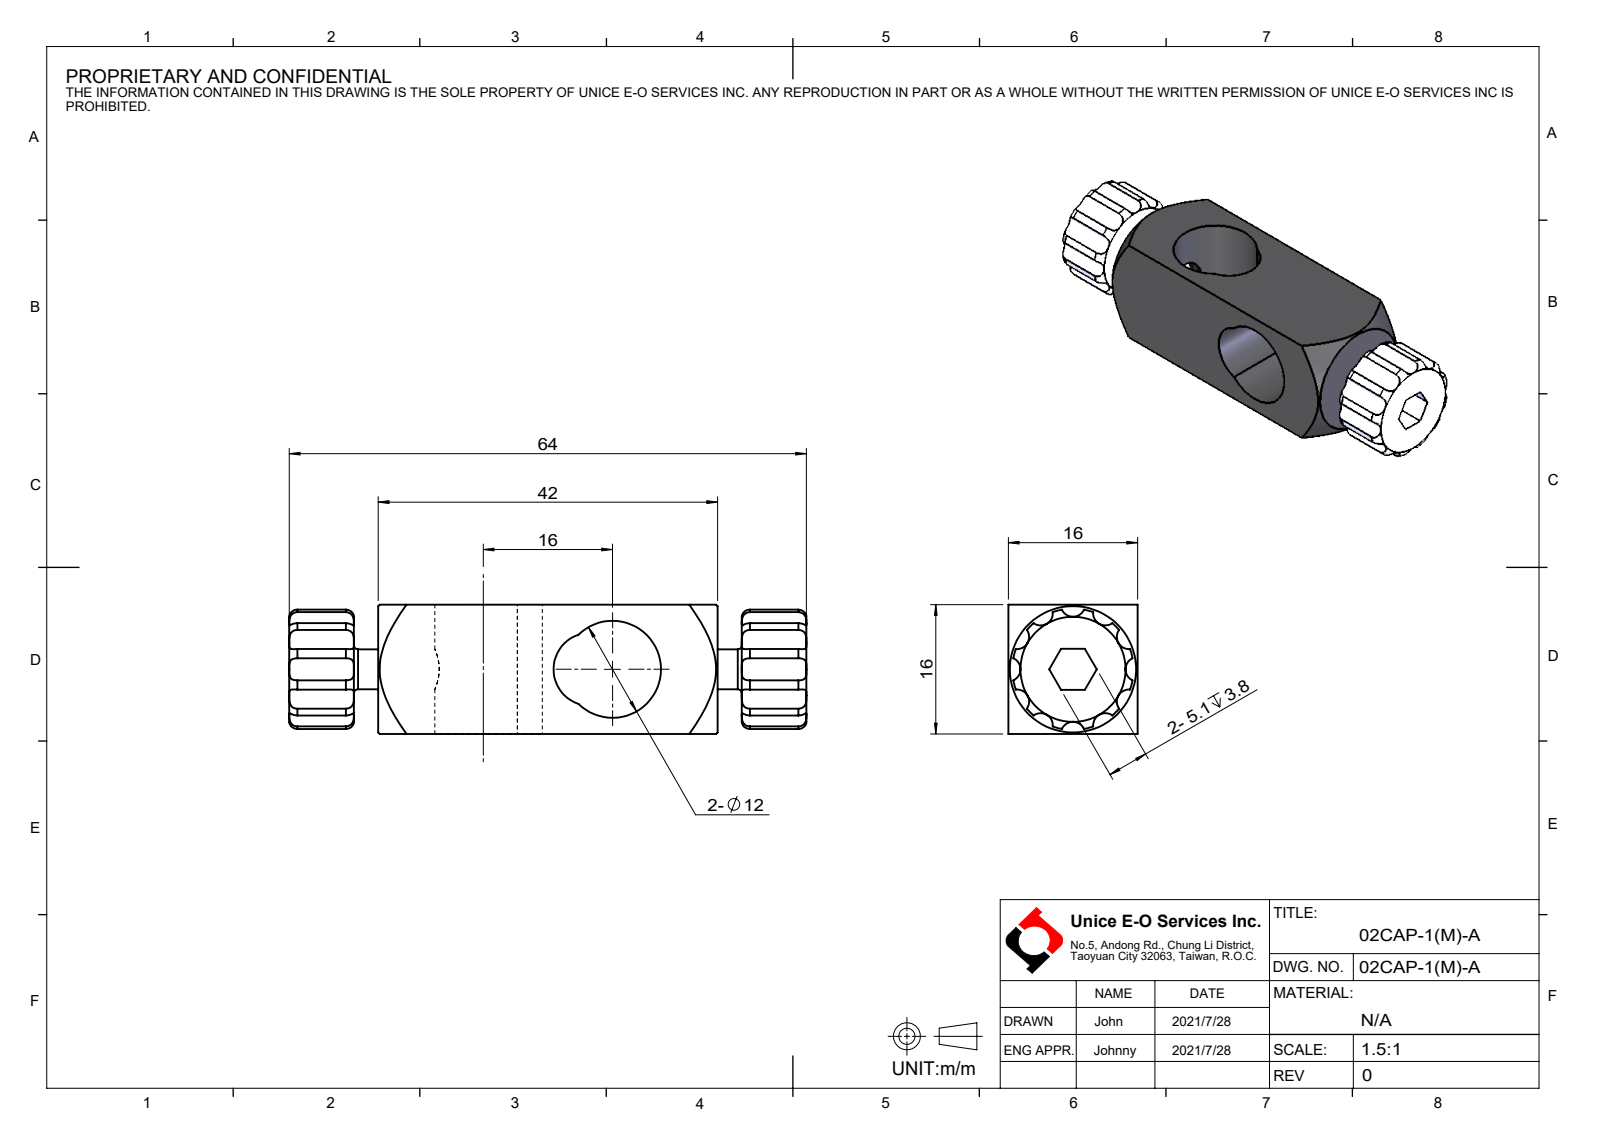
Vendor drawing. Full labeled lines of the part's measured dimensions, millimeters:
Part name (STEP PRODUCT): 02CAP-1(M)-A
STEP written by: SolidWorks 2020 (CONFIG_CONTROL_DESIGN)
Units: millimetres
Bodies: 3 solids, 158 faces (24 planar, 74 cylindrical, 60 other)
Overall size (bounding box): 64 × 16 × 16
Volume: 9 063 mm³ · Surface area: 5 855 mm²
Round holes (diameter × count): ⌀5 ×1
Round bosses / shafts (diameter × count): ⌀4.94 ×1
Partial cylindrical surfaces — rounded edges, fillets, slot ends (radius × count): R1.5 ×24, R4.5 ×2, R6 ×2, R7.5 ×1
Main face-to-face distances: 16, 11, 53, 8, 56, 3, 45, 42, 64, 48
